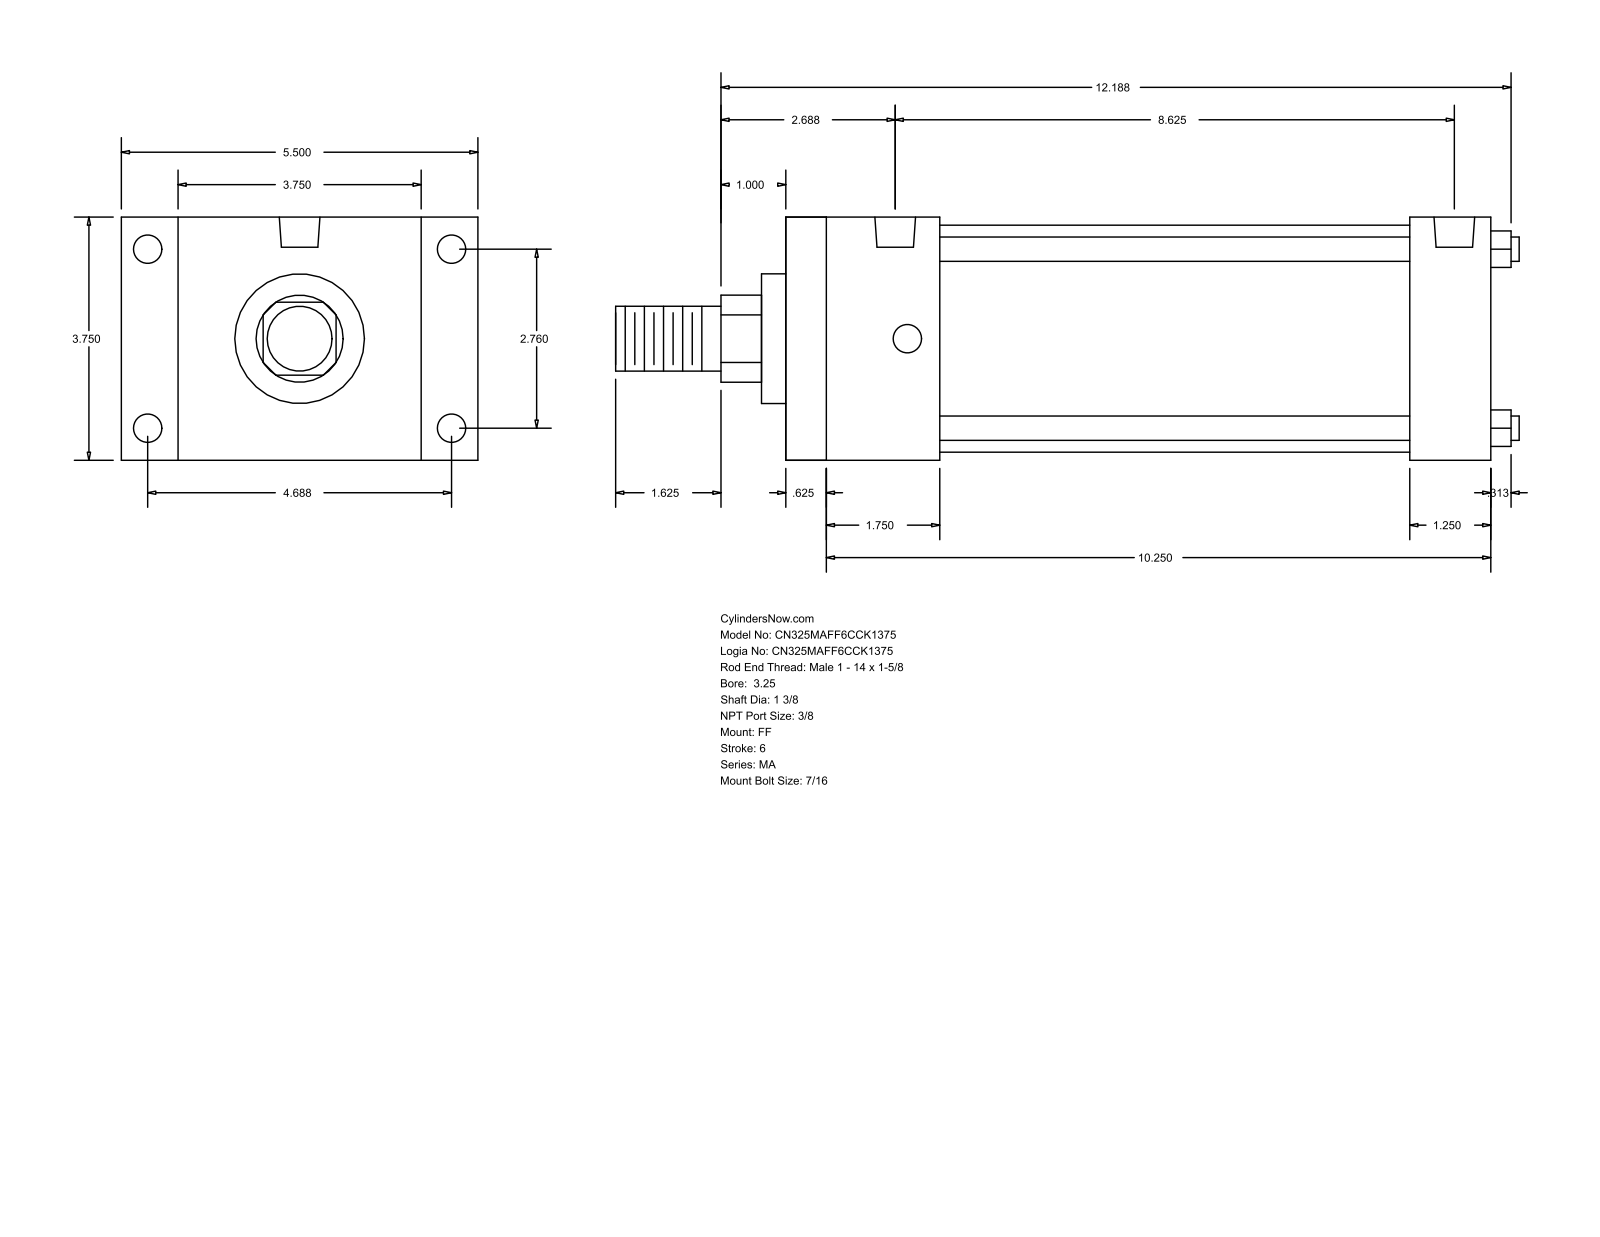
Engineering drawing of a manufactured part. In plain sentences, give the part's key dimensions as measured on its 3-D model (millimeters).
The part is named "MA_FF__0325_1.375". Its 3-D file was written by "GSSL Pune (CONFIG_CONTROL_DESIGN)". It is 0 solids with 92 faces: 64 planar, 28 cylindrical and 0 other. Overall it measures 354.01 by 139.7 by 95.25 millimeters. Round holes: 8 of diameter 11.11, 2 of diameter 15.93. Round bosses or shafts: 4 of diameter 9.53, 1 of diameter 88.9, 1 of diameter 50.8, 1 of diameter 34.92, 1 of diameter 25.4. Partial cylindrical surfaces (rounded edges, fillets, slot ends): 1 of radius 17.06. The main face-to-face distances are 95.24, 276.22, 15.87, 260.35, 22.23, 117.47, 60.32, 244.48, 44.45, 228.61. The hole center spacings are 4.77, 70.1, 119.06, 138.16, 209.54, 214.31, 219.08.
